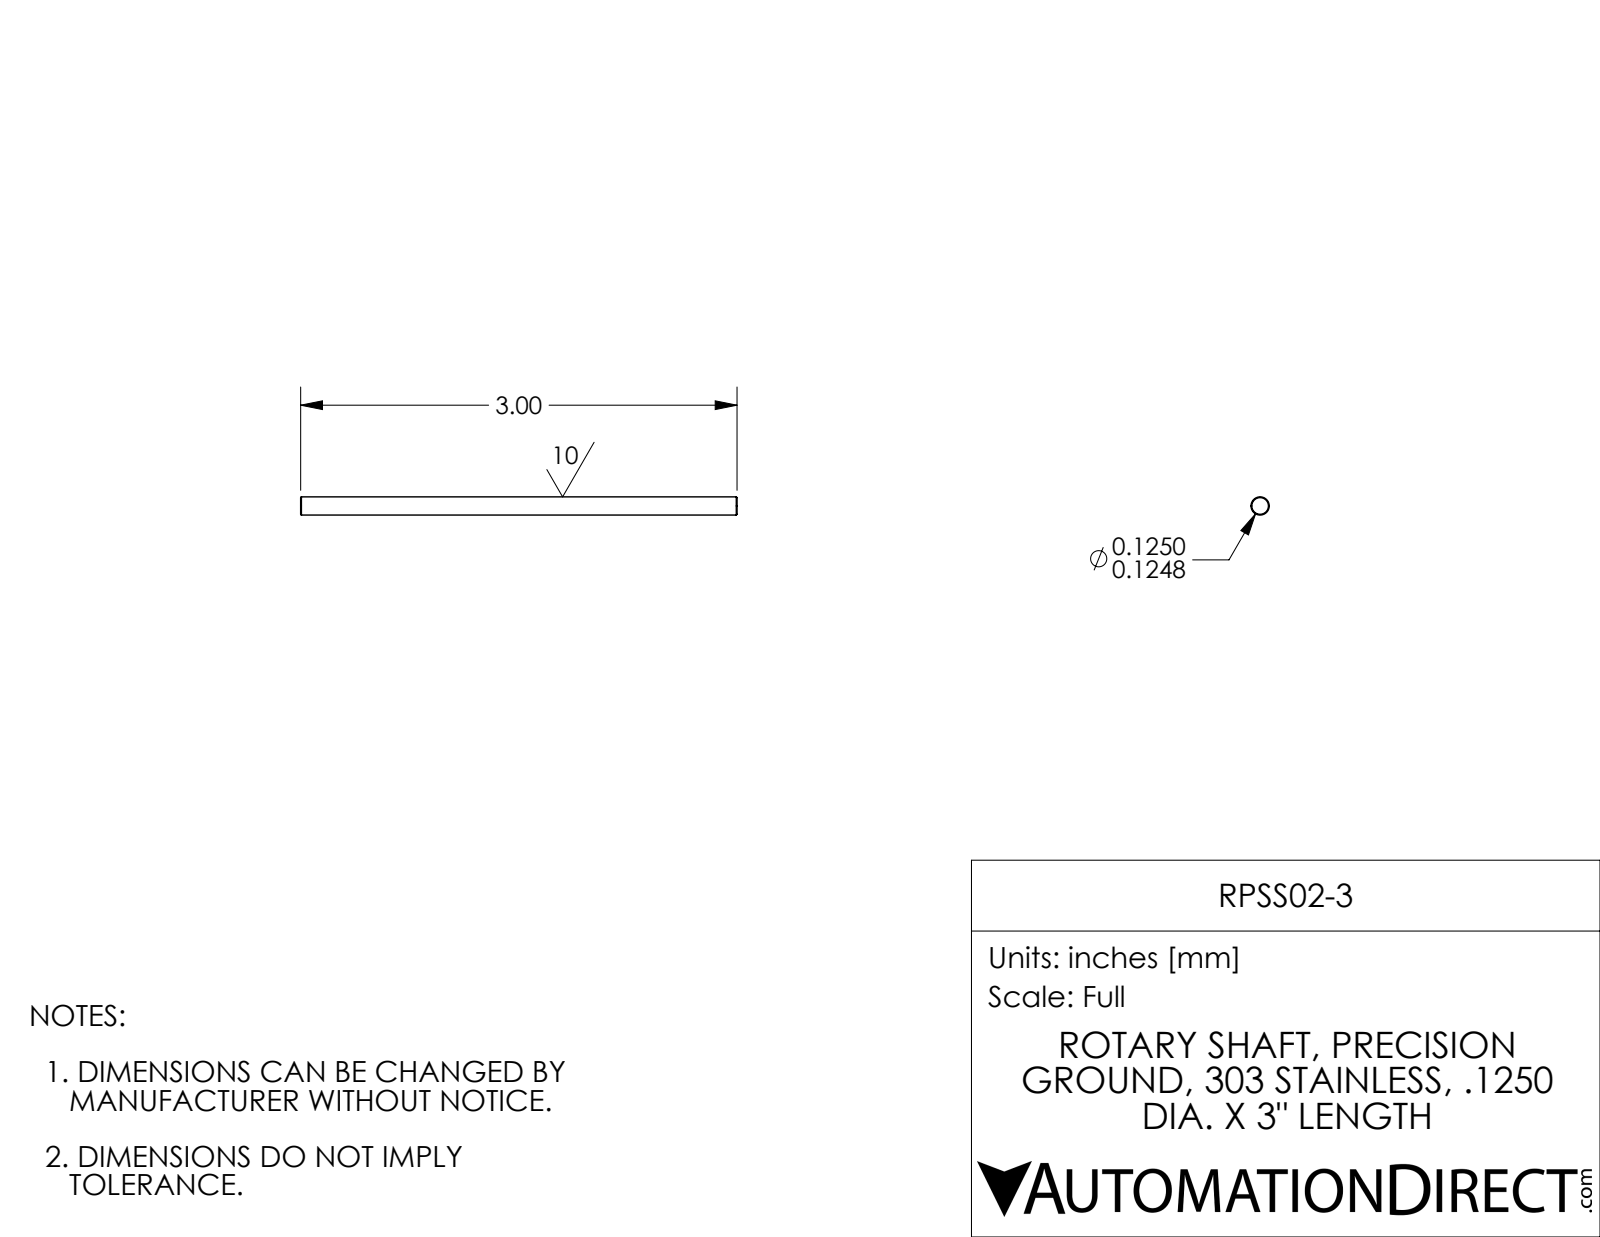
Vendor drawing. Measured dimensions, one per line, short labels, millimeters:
name: RPSS02-3
written by: SolidWorks 2017 (AUTOMOTIVE_DESIGN)
unit: mm
bodies: 1 solid, 8 faces (2 planar, 2 cylindrical, 4 other)
size: 76.2 × 3.2 × 3.2
volume: 610 mm³; area: 774 mm²
bosses: 1× ⌀3.2
face distances: 76.2
